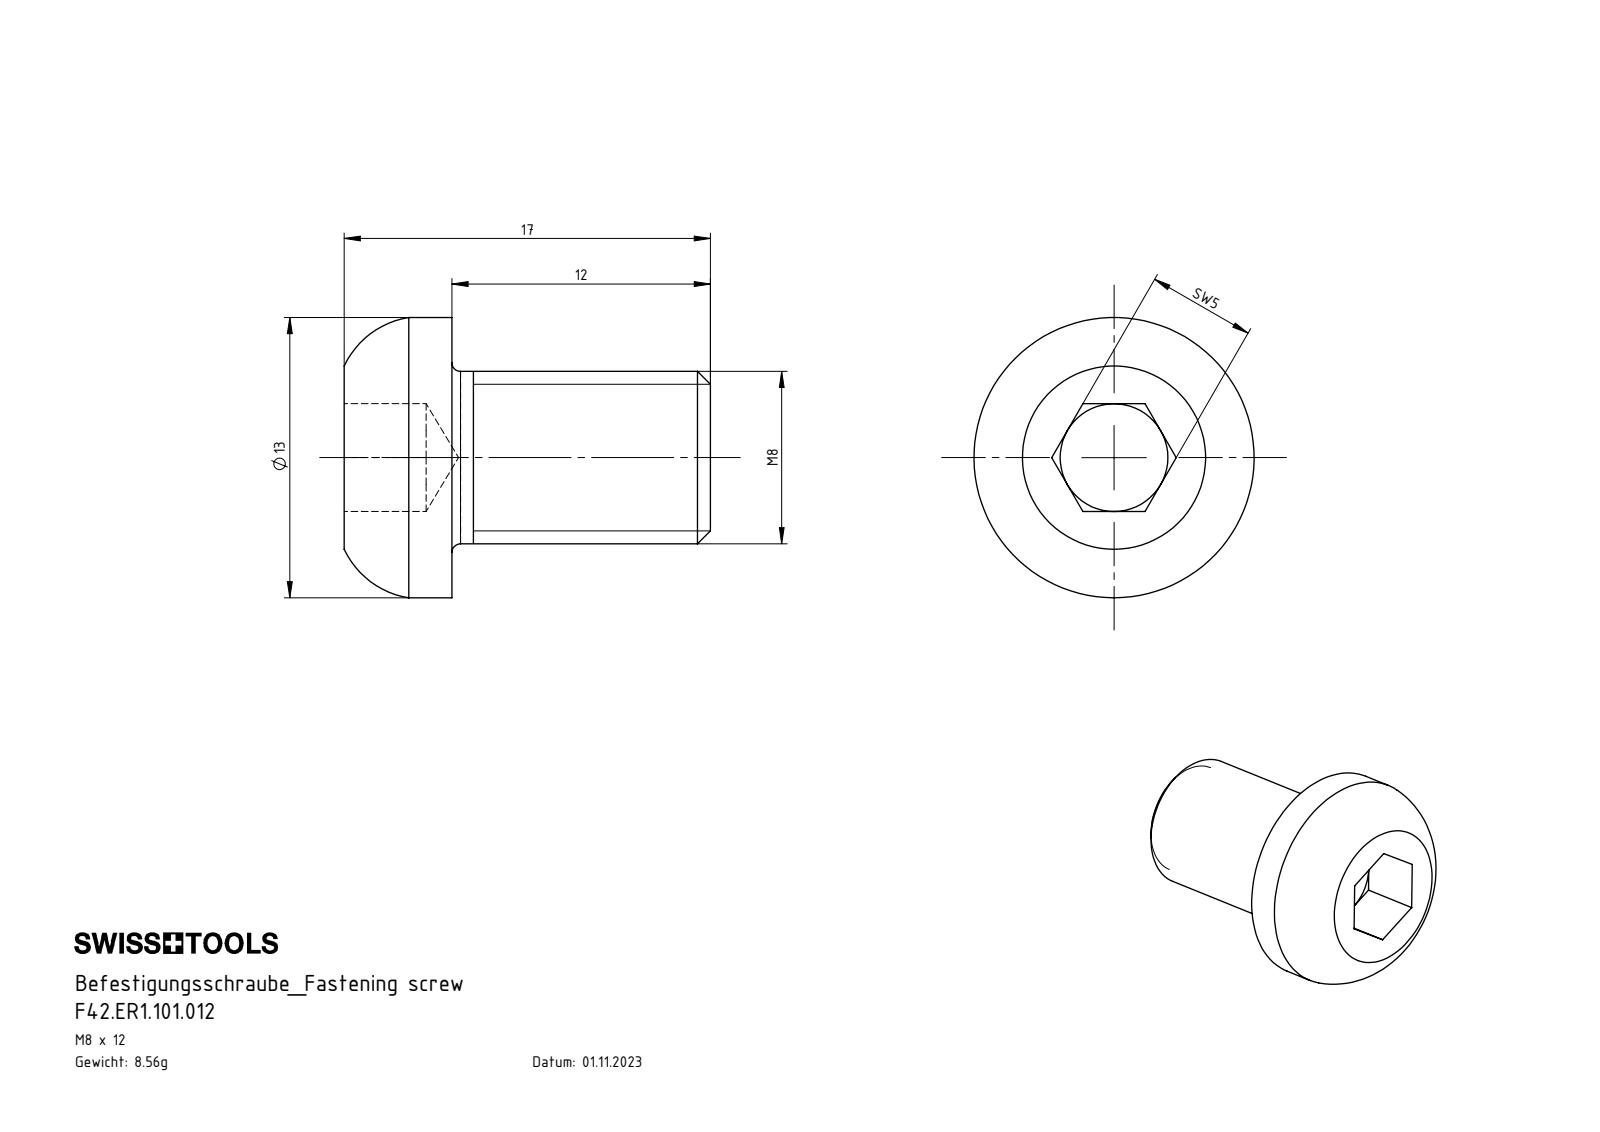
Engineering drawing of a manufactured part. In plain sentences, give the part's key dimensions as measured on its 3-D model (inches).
The part is named "F42.ER1.101.012". Its 3-D file was written by "SolidWorks 2017 (AUTOMOTIVE_DESIGN)". It is 1 solid with 27 faces: 15 planar, 4 cylindrical and 8 other. Overall it measures 0.669 by 0.512 by 0.512 inches. Its volume is 0.067 cubic inches and its surface area 1.19 square inches. Round bosses or shafts: 1 of diameter 0.512, 1 of diameter 0.315. The main face-to-face distances are 0.197, 0.472, 0.669, 0.15, 0.047, 0.52.
